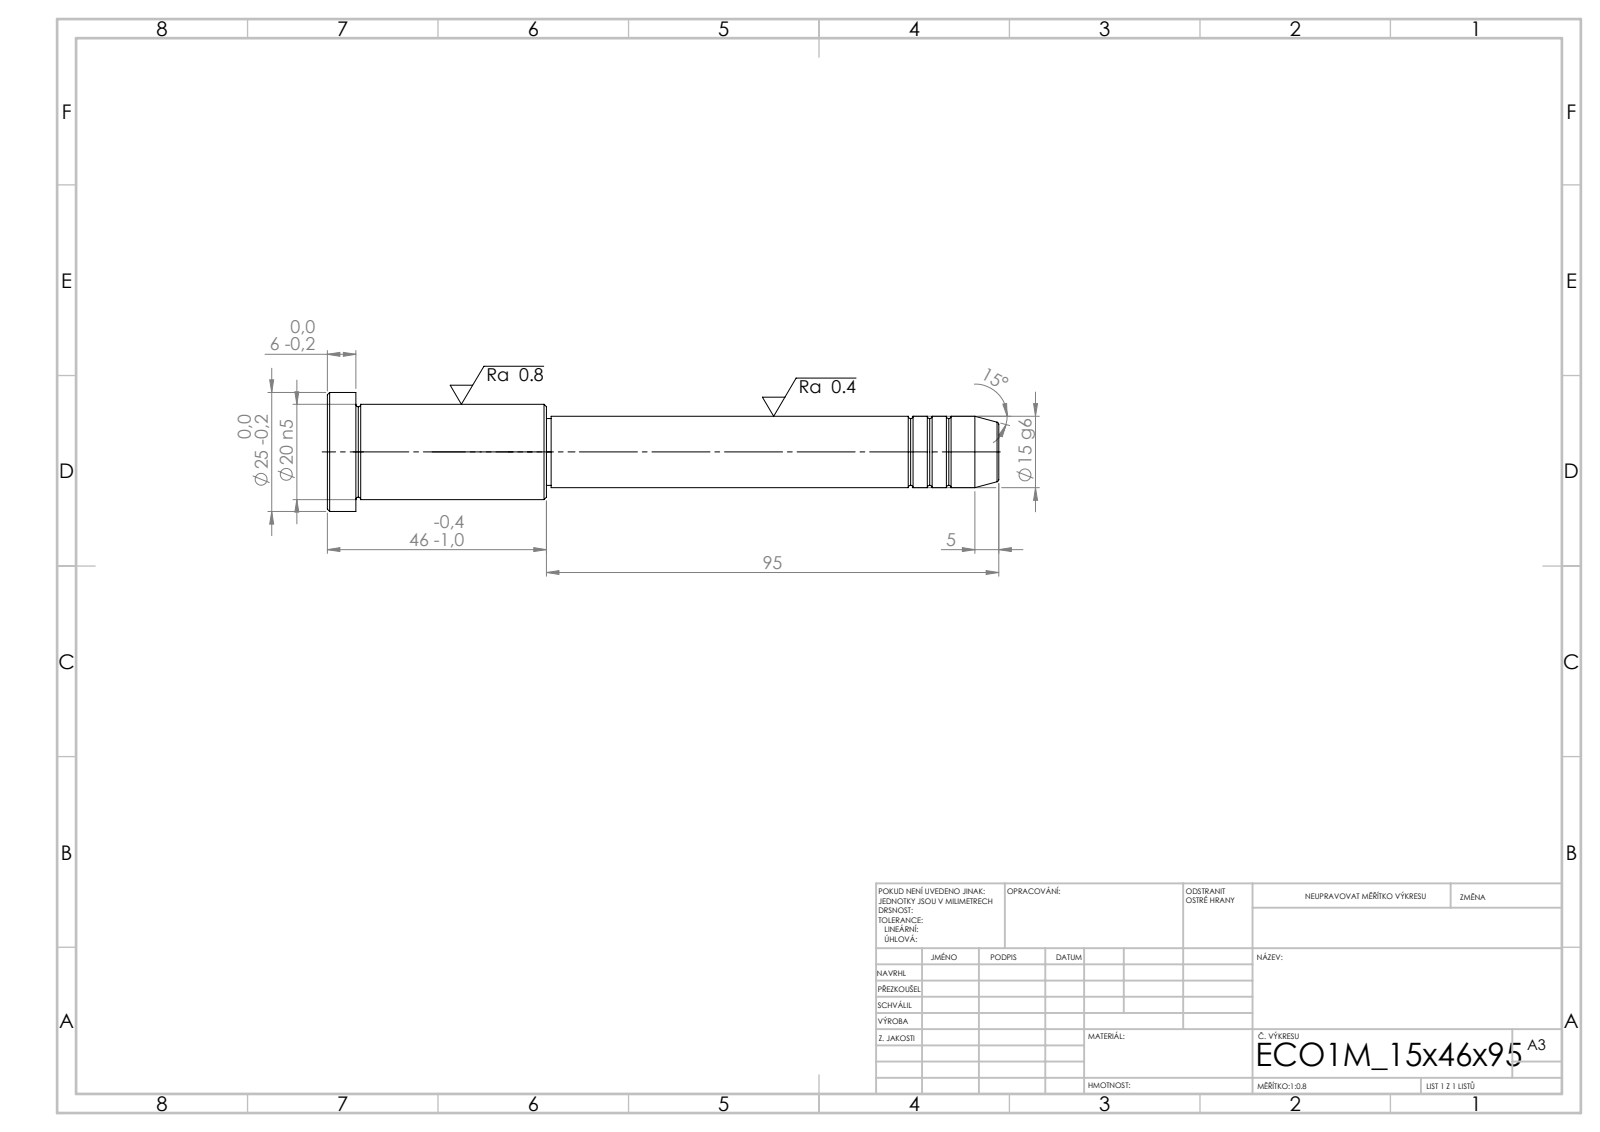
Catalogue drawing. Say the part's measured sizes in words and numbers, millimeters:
Its 3-D file was written by "SolidWorks 2019 (CONFIG_CONTROL_DESIGN)". It is 1 solid with 43 faces: 5 planar, 14 cylindrical and 24 other. Overall it measures 141 by 25 by 25 millimeters. Its volume is 32 032 cubic millimeters and its surface area 8 472 square millimeters. Round bosses or shafts: 1 of diameter 25, 1 of diameter 20, 1 of diameter 15, 1 of diameter 14. The main face-to-face distances are 6, 40, 46, 95, 135, 141, 94, 1, 41, 47.
